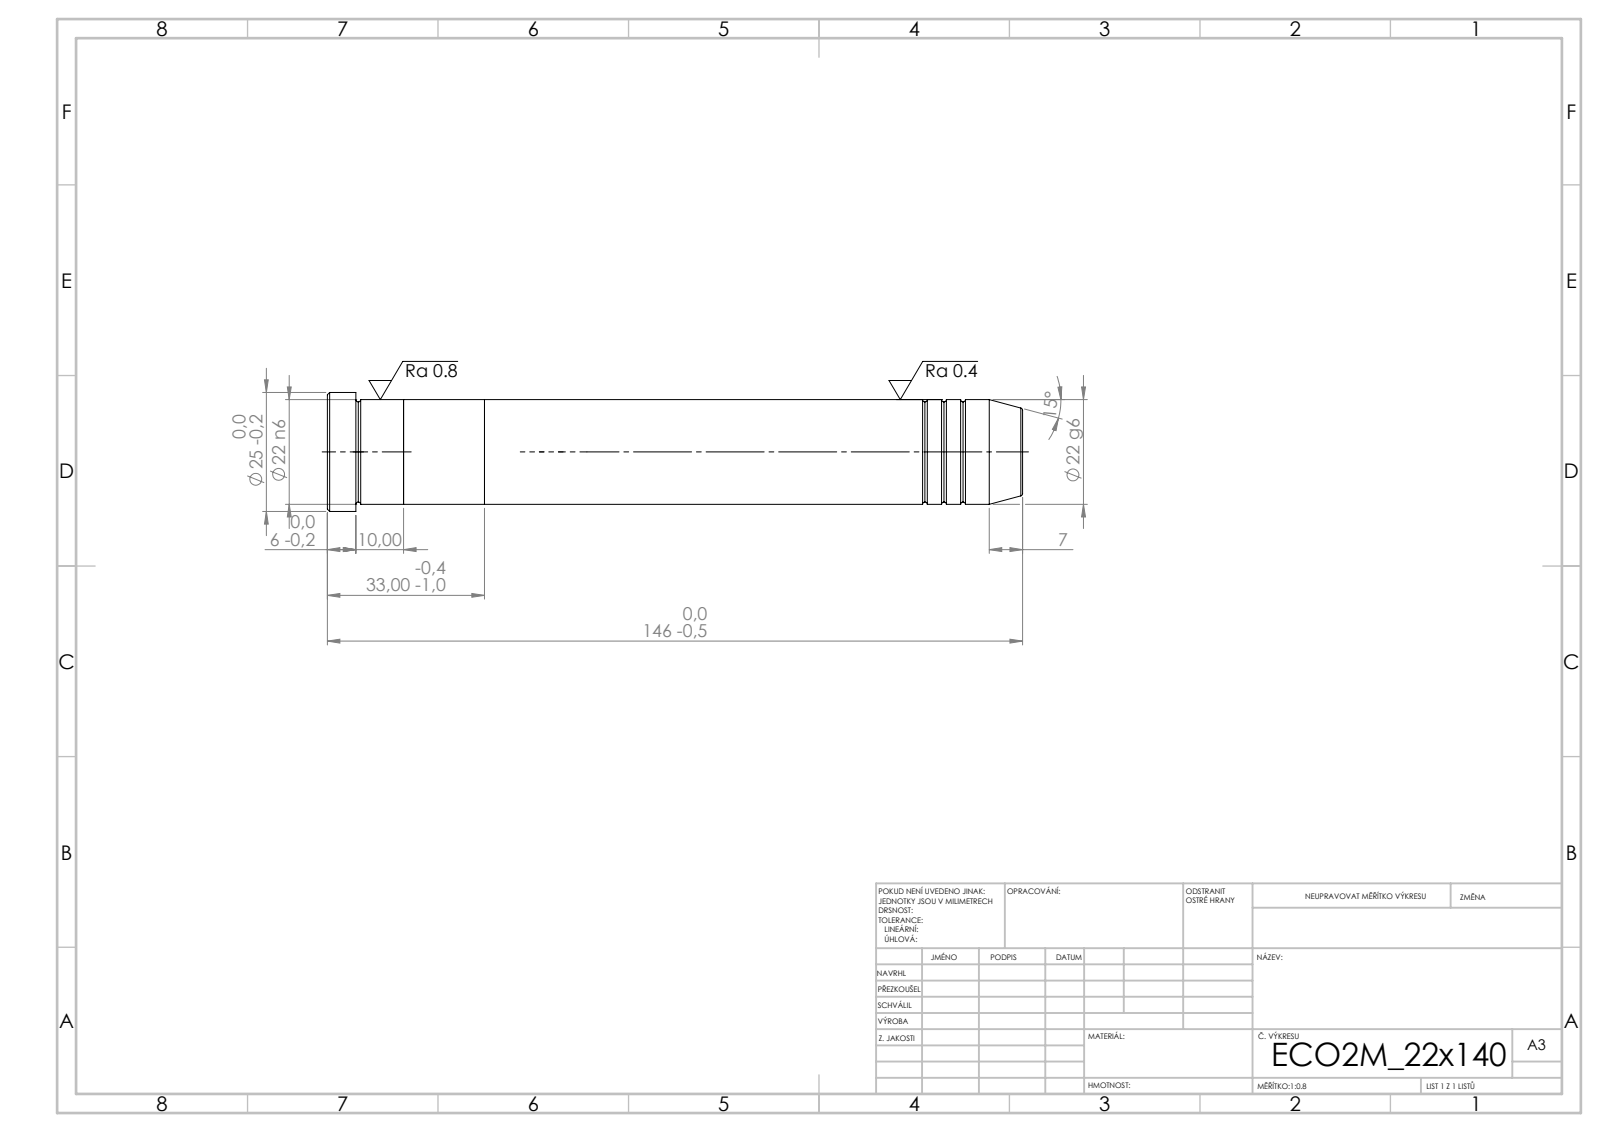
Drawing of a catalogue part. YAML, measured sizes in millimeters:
step_written_by: "SolidWorks 2019 (CONFIG_CONTROL_DESIGN)"
units: millimeters
bodies: {solids: 3, faces: 43, planar: 7, cylindrical: 14, other: 22}
overall_size: [146, 25, 25]
volume: 55618
surface_area: 12621
round_bosses_or_shafts:
  - {diameter: 25, count: 1}
  - {diameter: 22, count: 1}
face_to_face_distances: [17, 33, 16, 113, 130, 146, 140, 27, 10, 6]
